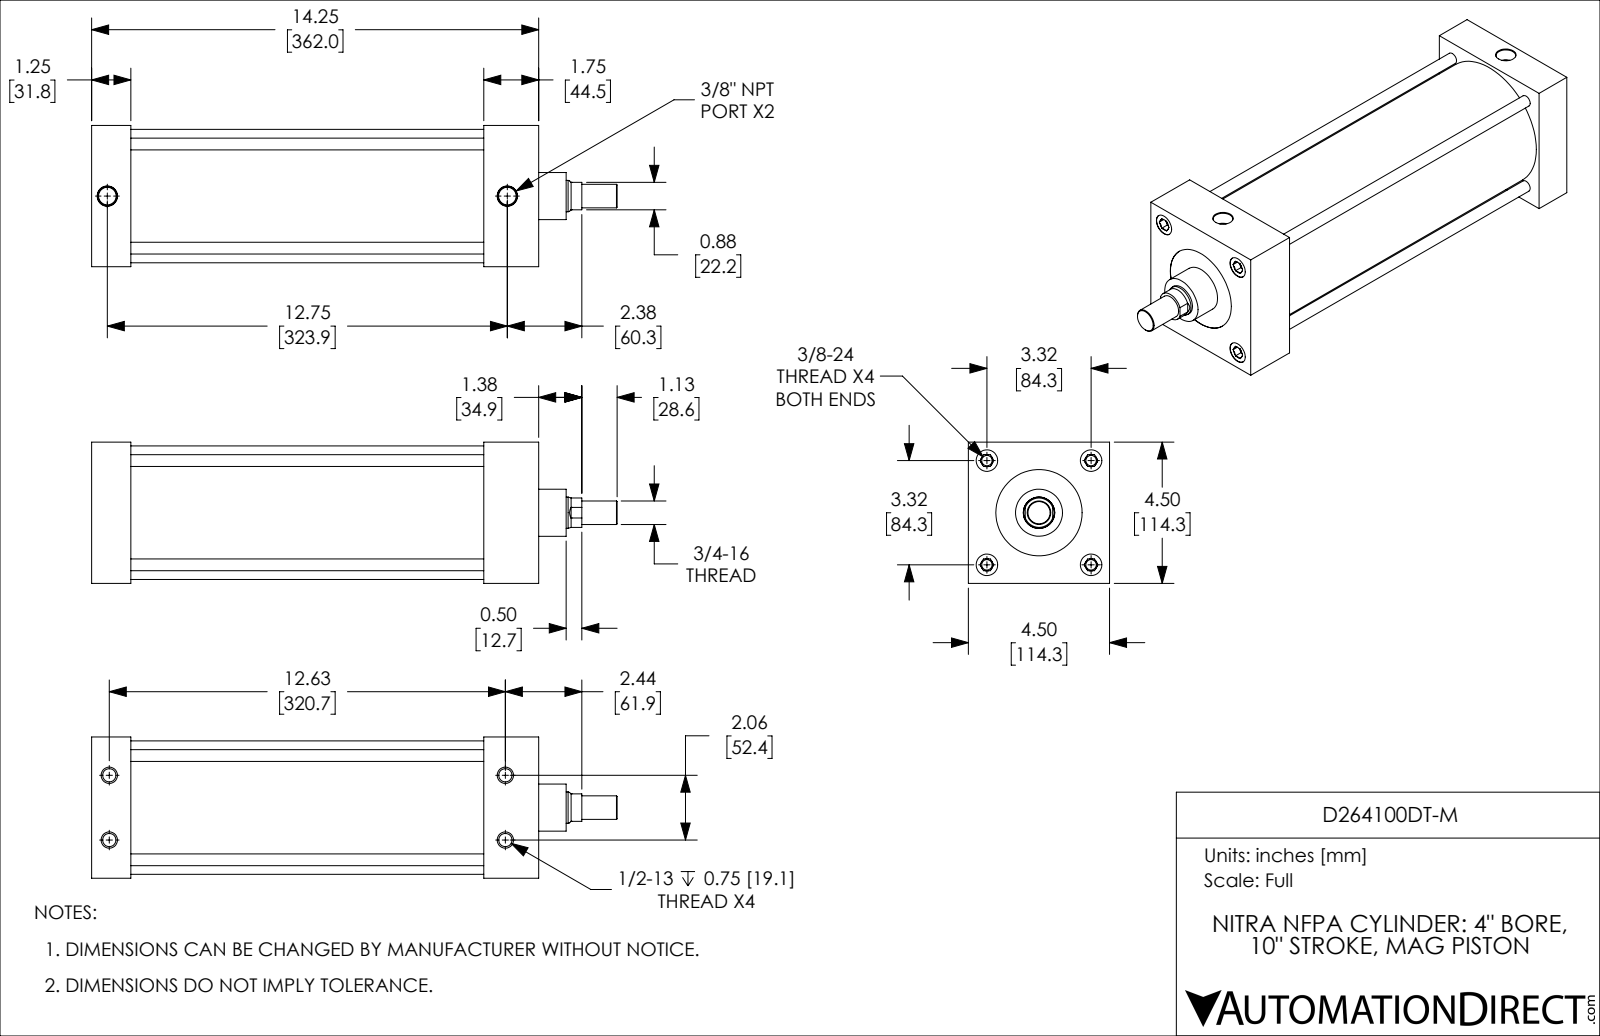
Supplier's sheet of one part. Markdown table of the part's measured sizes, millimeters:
| quantity | value |
| --- | --- |
| part name | D264100DT-M_PISTON_KK1; D264100DT-M; D264100DT-M_BODY |
| STEP written by | SolidWorks 2019 (CONFIG_CONTROL_DESIGN) |
| units | millimeters |
| bodies | 2 solids, 198 faces (58 planar, 62 cylindrical, 78 other) |
| overall size | 425.5 × 114.3 × 114.3 |
| volume | 1 762 000 mm³ |
| surface area | 381 200 mm² |
| round holes (diameter × count) | 8.4 × 4, 10.7 × 4, 17.4 × 4, 14.3 × 2, 25.4 × 1, 69.9 × 1, 101.6 × 1 |
| round bosses / shafts (diameter × count) | 9.5 × 4, 108 × 1, 101.6 × 1, 38.1 × 1, 25.4 × 1, 19.1 × 1 |
| partial cylindrical surfaces (radius × count) | 11.9 × 1 |
| main face-to-face distances | 31.8, 114.3, 317.5, 285.8, 362, 330.2, 44.5, 63.5, 254, 298.5 |
| hole center spacings | 59.6, 84.3, 323.3, 26.2, 119.3, 320.7, 324.9, 26.3 |
